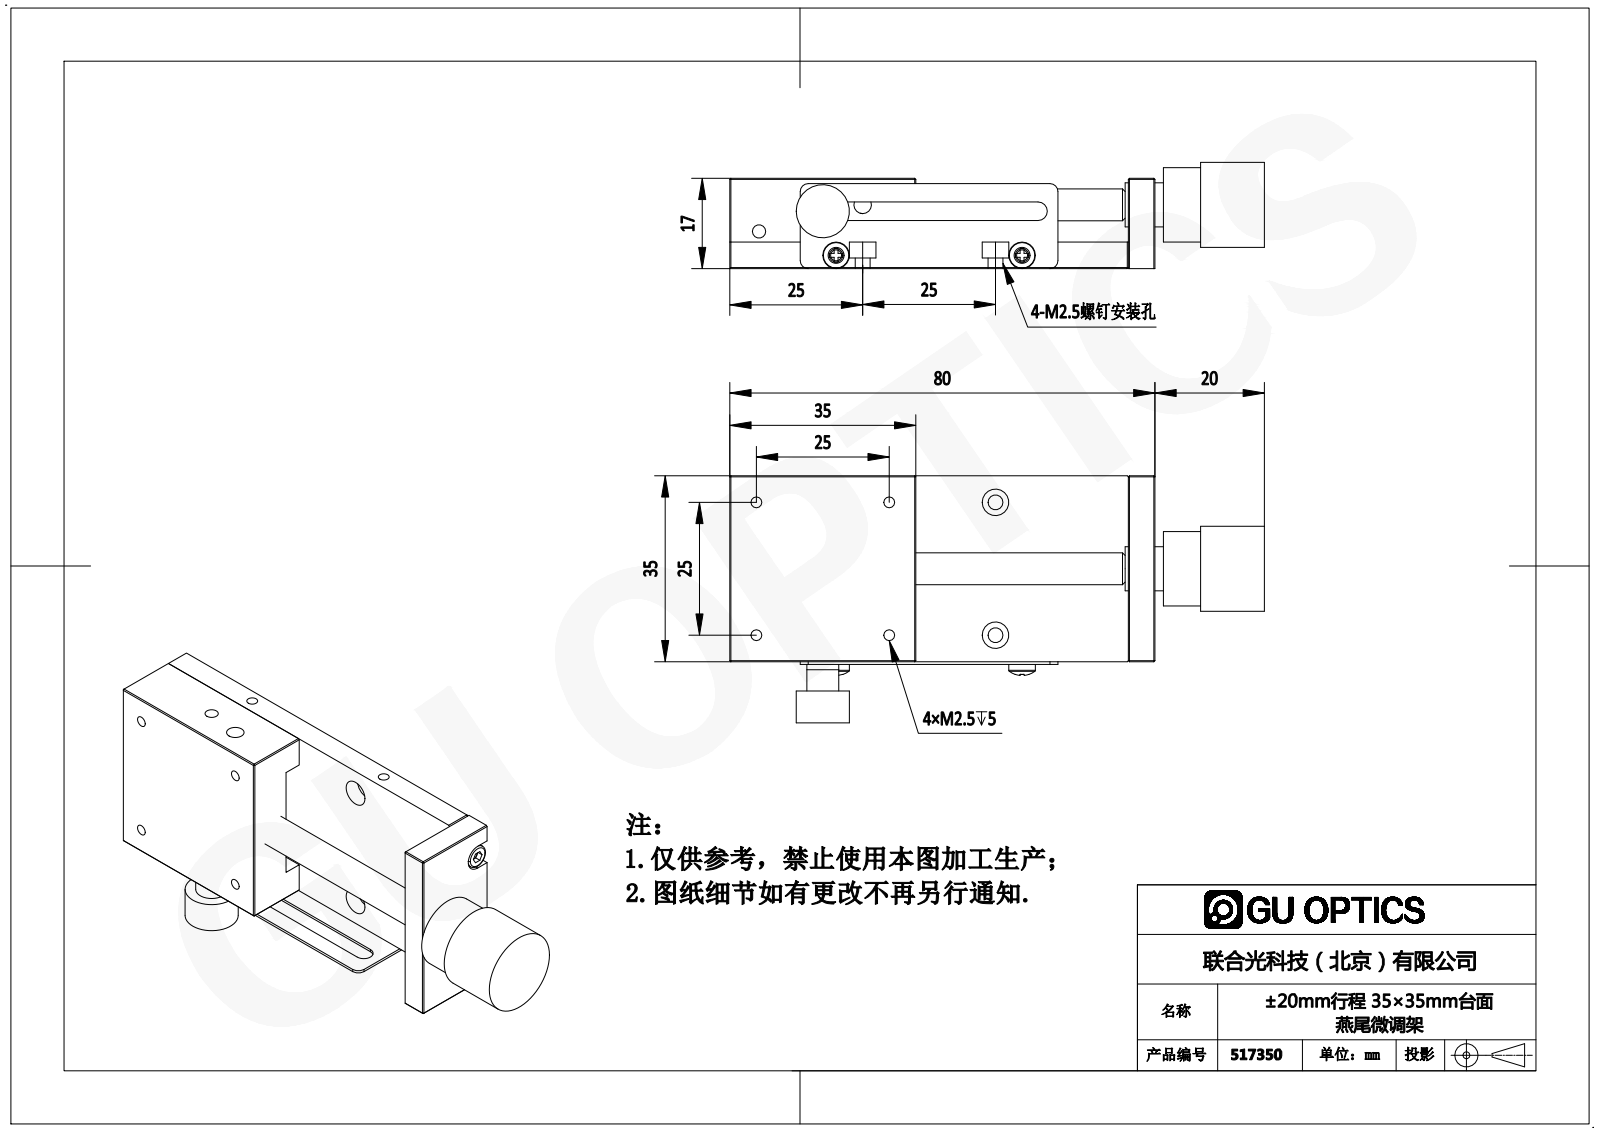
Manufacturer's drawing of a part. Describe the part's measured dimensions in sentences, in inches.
The part is named "517350". Its 3-D file was written by "SolidWorks 2016 (AUTOMOTIVE_DESIGN)". It is 9 solids with 300 faces: 146 planar, 106 cylindrical and 48 other. Overall it measures 3.961 by 1.831 by 0.787 inches. Its volume is 1.976 cubic inches and its surface area 28.65 square inches. Round holes: 8 of diameter 0.081, 5 of diameter 0.118, 5 of diameter 0.197, 4 of diameter 0.098, 4 of diameter 0.11, 1 of diameter 0.13, 1 of diameter 0.256. Round bosses or shafts: 4 of diameter 0.098, 2 of diameter 0.236, 2 of diameter 0.197, 2 of diameter 0.177, 1 of diameter 0.63, 1 of diameter 0.551, 1 of diameter 0.394, 1 of diameter 0.327. Partial cylindrical surfaces (rounded edges, fillets, slot ends): 4 of radius 0.059, 2 of radius 0.069, 2 of radius 0.098. The main face-to-face distances are 0.197, 0.335, 0.472, 0.669, 1.378, 0.138, 1.398, 0.02, 3.15, 2.953. The hole center spacings are 0.984, 0.787, 1.261, 1.392, 0.197, 0.472, 0.496, 0.587.
